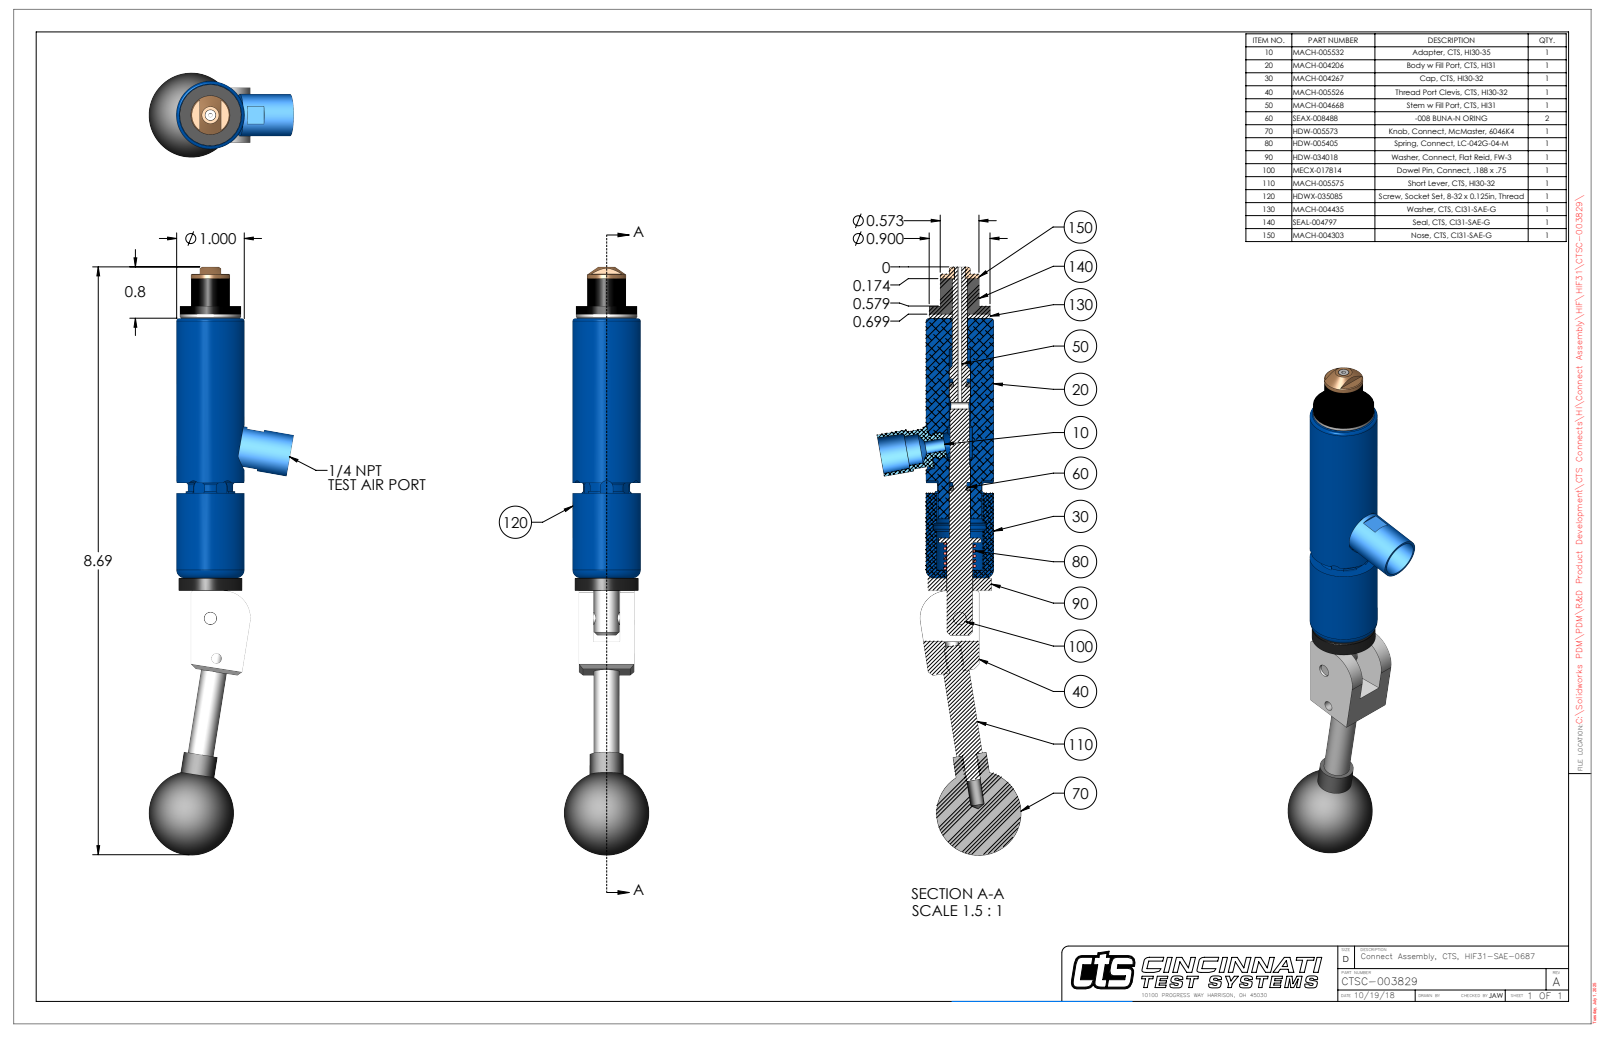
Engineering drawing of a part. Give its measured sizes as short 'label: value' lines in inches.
name: CTSC-003829
written by: SolidWorks 2023 (AUTOMOTIVE_DESIGN)
unit: in
bodies: 9 solids, 302 faces (115 planar, 122 cylindrical, 65 other)
size: 8.692 × 2.128 × 1.25
volume: 5.196 in³; area: 40.76 in²
holes: 2× ⌀0.201, 1× ⌀0.063, 1× ⌀0.109, 1× ⌀0.136, 1× ⌀0.15, 1× ⌀0.159, 1× ⌀0.187, 1× ⌀0.189, 1× ⌀0.218, 1× ⌀0.228, 1× ⌀0.229, 1× ⌀0.385
bosses: 1× ⌀1, 1× ⌀0.936, 1× ⌀0.9, 1× ⌀0.62, 1× ⌀0.573, 1× ⌀0.5, 1× ⌀0.38, 1× ⌀0.375
rounds: 6× R0.093, 2× R0.029, 1× R0.064, 1× R0.325, 1× R0.375, 1× R0.4, 1× R0.458
face distances: 0.21, 0.602, 0.06, 3.896, 3.835, 0.812, 4.083, 4.023, 0.187, 0.391
hole spacings: 0.599, 1.658, 2.252
